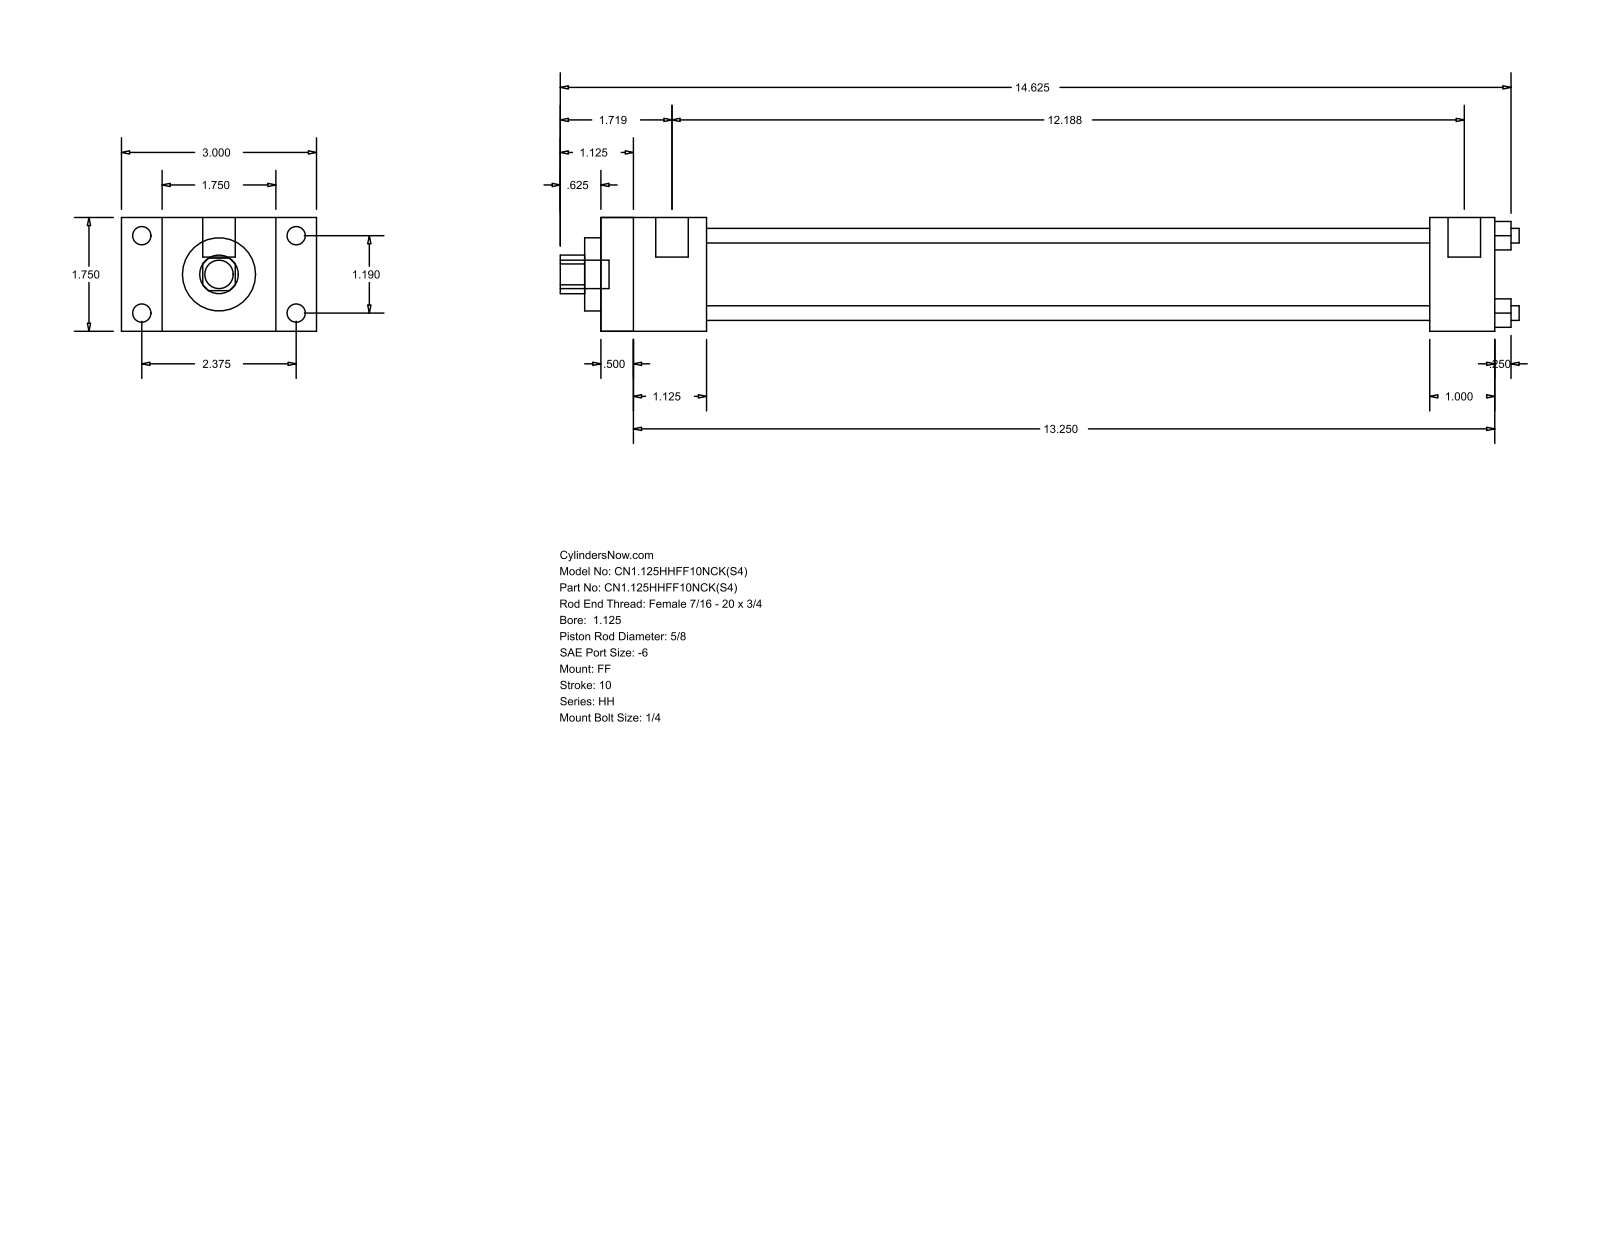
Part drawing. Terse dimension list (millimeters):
name: HH_FF__0112_0.625
written by: GSSL Pune (CONFIG_CONTROL_DESIGN)
unit: mm
bodies: 0 solids, 92 faces (64 planar, 28 cylindrical, 0 other)
size: 374.65 × 76.2 × 44.45
holes: 4× ⌀5.71, 1× ⌀15.88, 1× ⌀28.57, 1× ⌀34.92
bosses: 4× ⌀7.14, 4× ⌀5.56, 2× ⌀12.7, 1× ⌀11.11
rounds: 1× R7.54
face distances: 44.46, 349.24, 15.87, 12.69, 336.55, 60.33, 28.58, 41.27, 323.85, 311.16
hole spacings: 21.37, 30.22, 42.74
